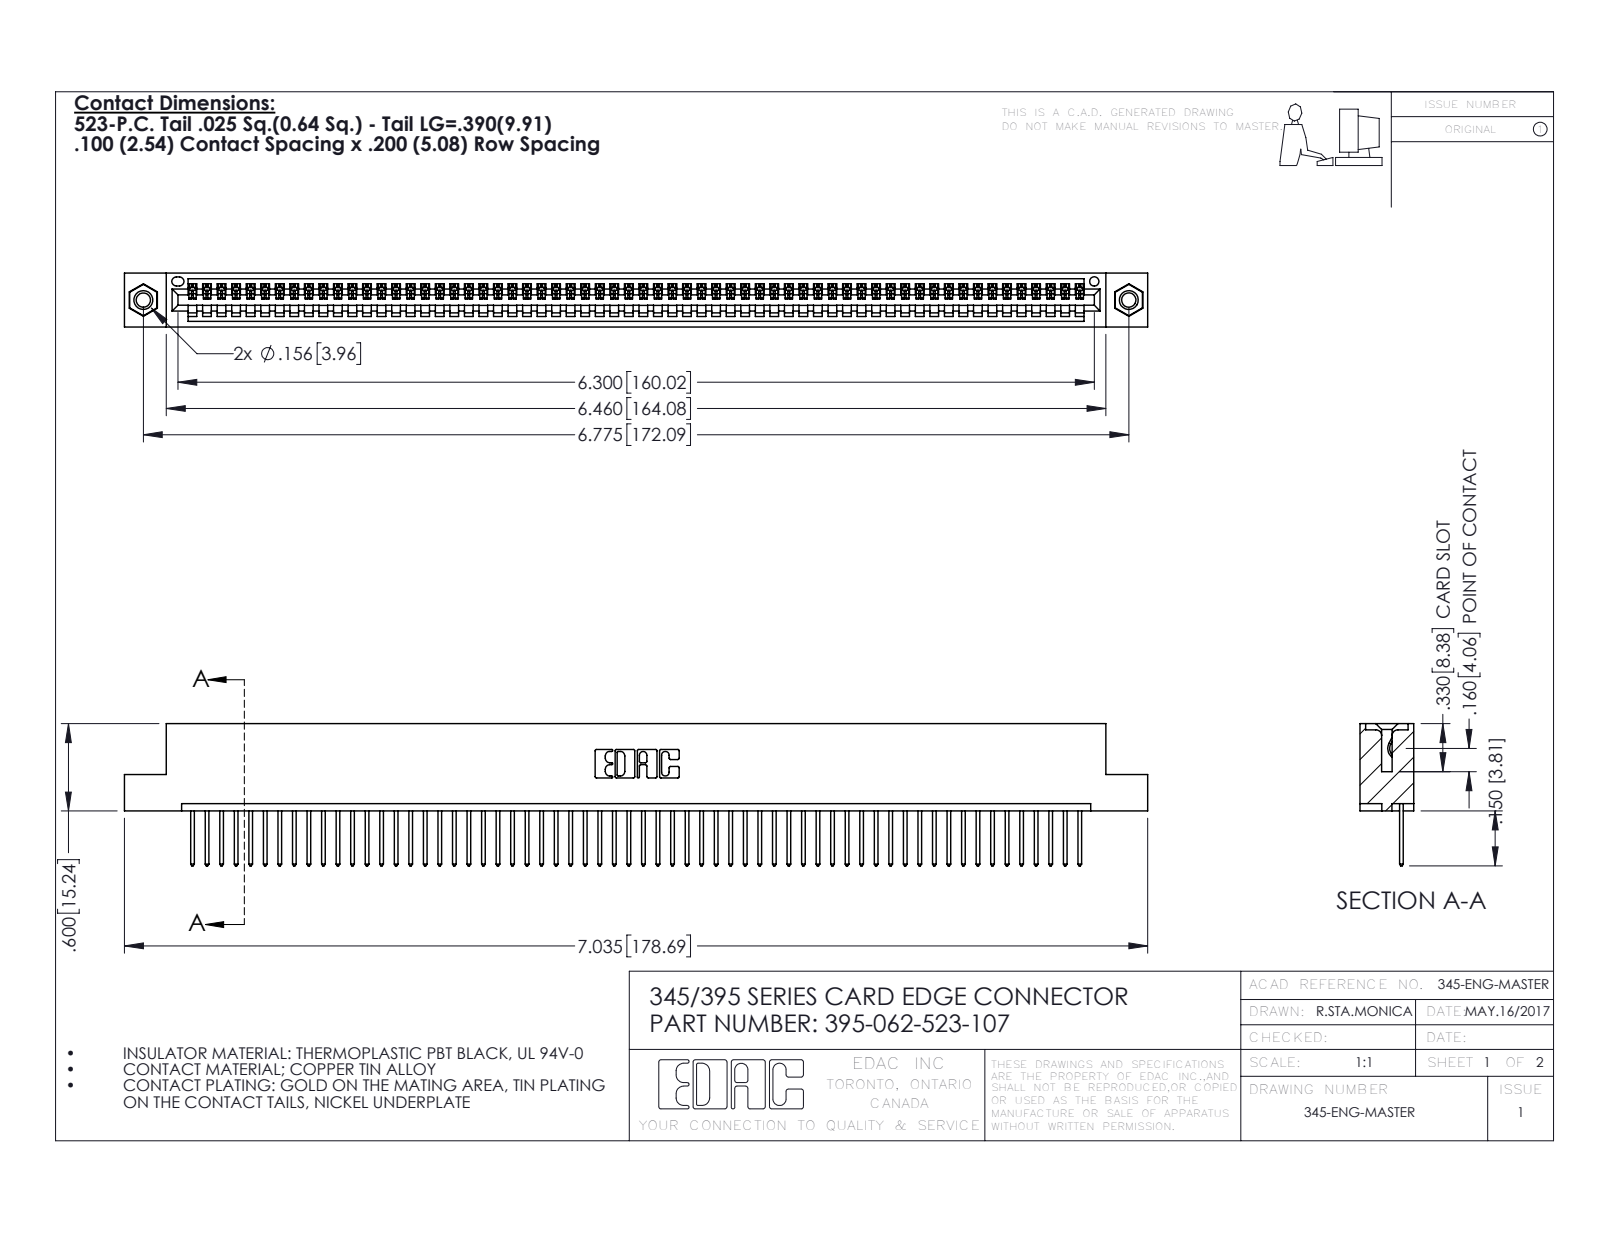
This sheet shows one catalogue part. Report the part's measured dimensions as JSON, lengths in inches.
{"part_name": "345-250-001_345-250-005-103; 345-292-001_345-293-123; 395-062-523-107; 345 Part_Flush Mounting Lugs - 0.156 Dia-TI", "step_written_by": "SolidWorks 2016 (CONFIG_CONTROL_DESIGN)", "units": "inches", "bodies": {"solids": 65, "faces": 3782, "planar": 2592, "cylindrical": 1174, "other": 16}, "overall_size": [7.035, 0.977, 0.37], "volume_in3": 1.043, "surface_area_in2": 35.8, "round_holes": [[0.098, 2], [0.125, 2], [0.156, 2], [0.064, 1]], "round_bosses_or_shafts": [[0.155, 2]], "partial_cylinders_radius": [[0.006, 124], [0.01, 124], [0.01, 22], [0.007, 6], [0.031, 6], [0.026, 3], [0.031, 2], [0.04, 2]], "face_to_face_distances": [0.072, 0.298, 0.37, 0.2, 0.098, 0.272, 0.025, 0.225, 0.149, 0.072], "hole_center_spacings": [0.27, 6.539, 6.775]}
